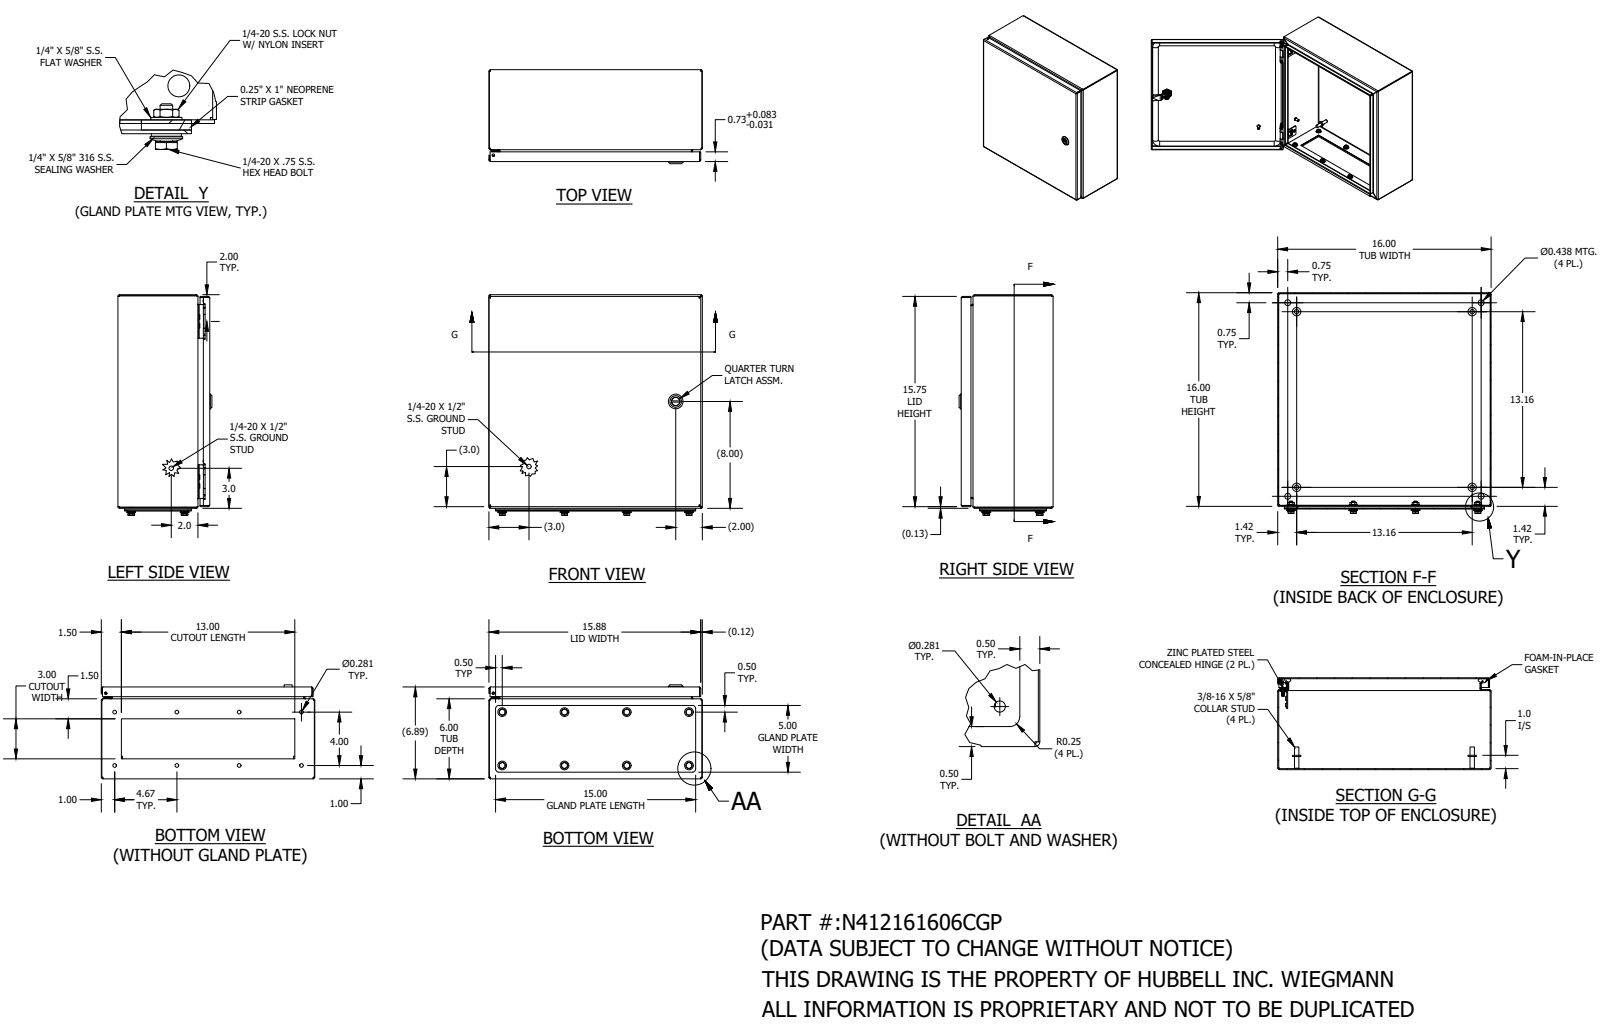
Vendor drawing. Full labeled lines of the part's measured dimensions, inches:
Part name (STEP PRODUCT): N412161606CGP
STEP written by: SolidWorks 2019 (AUTOMOTIVE_DESIGN)
Units: inches
Bodies: 71 solids, 2035 faces (794 planar, 624 cylindrical, 617 other)
Overall size (bounding box): 16.519 × 16 × 7.044
Volume: 97.19 in³ · Surface area: 2 367 in²
Round holes (diameter × count): ⌀0.281 ×10, ⌀0.16 ×8, ⌀0.211 ×8, ⌀0.29 ×8, ⌀0.35 ×6, ⌀0.188 ×5, ⌀0.093 ×4, ⌀0.167 ×4, ⌀0.235 ×4, ⌀0.235 ×4, ⌀0.275 ×4, ⌀0.275 ×4
Round bosses / shafts (diameter × count): ⌀0.25 ×18, ⌀0.65 ×8, ⌀0.6 ×8, ⌀0.438 ×8, ⌀0.625 ×7, ⌀0.625 ×5, ⌀0.131 ×5, ⌀0.36 ×4
Partial cylindrical surfaces — rounded edges, fillets, slot ends (radius × count): R0.012 ×30, R0.05 ×26, R0.047 ×20, R0.121 ×20, R0.02 ×13, R0.125 ×8, R0.13 ×8, R0.157 ×5
Main face-to-face distances: 0.074, 6.812, 6.738, 6.886, 16.13, 15.926, 15.852, 0.074, 15.926, 16
Hole centre spacings: 6.146, 0.66, 4, 12.004, 4.667, 11.344, 12, 12.002
